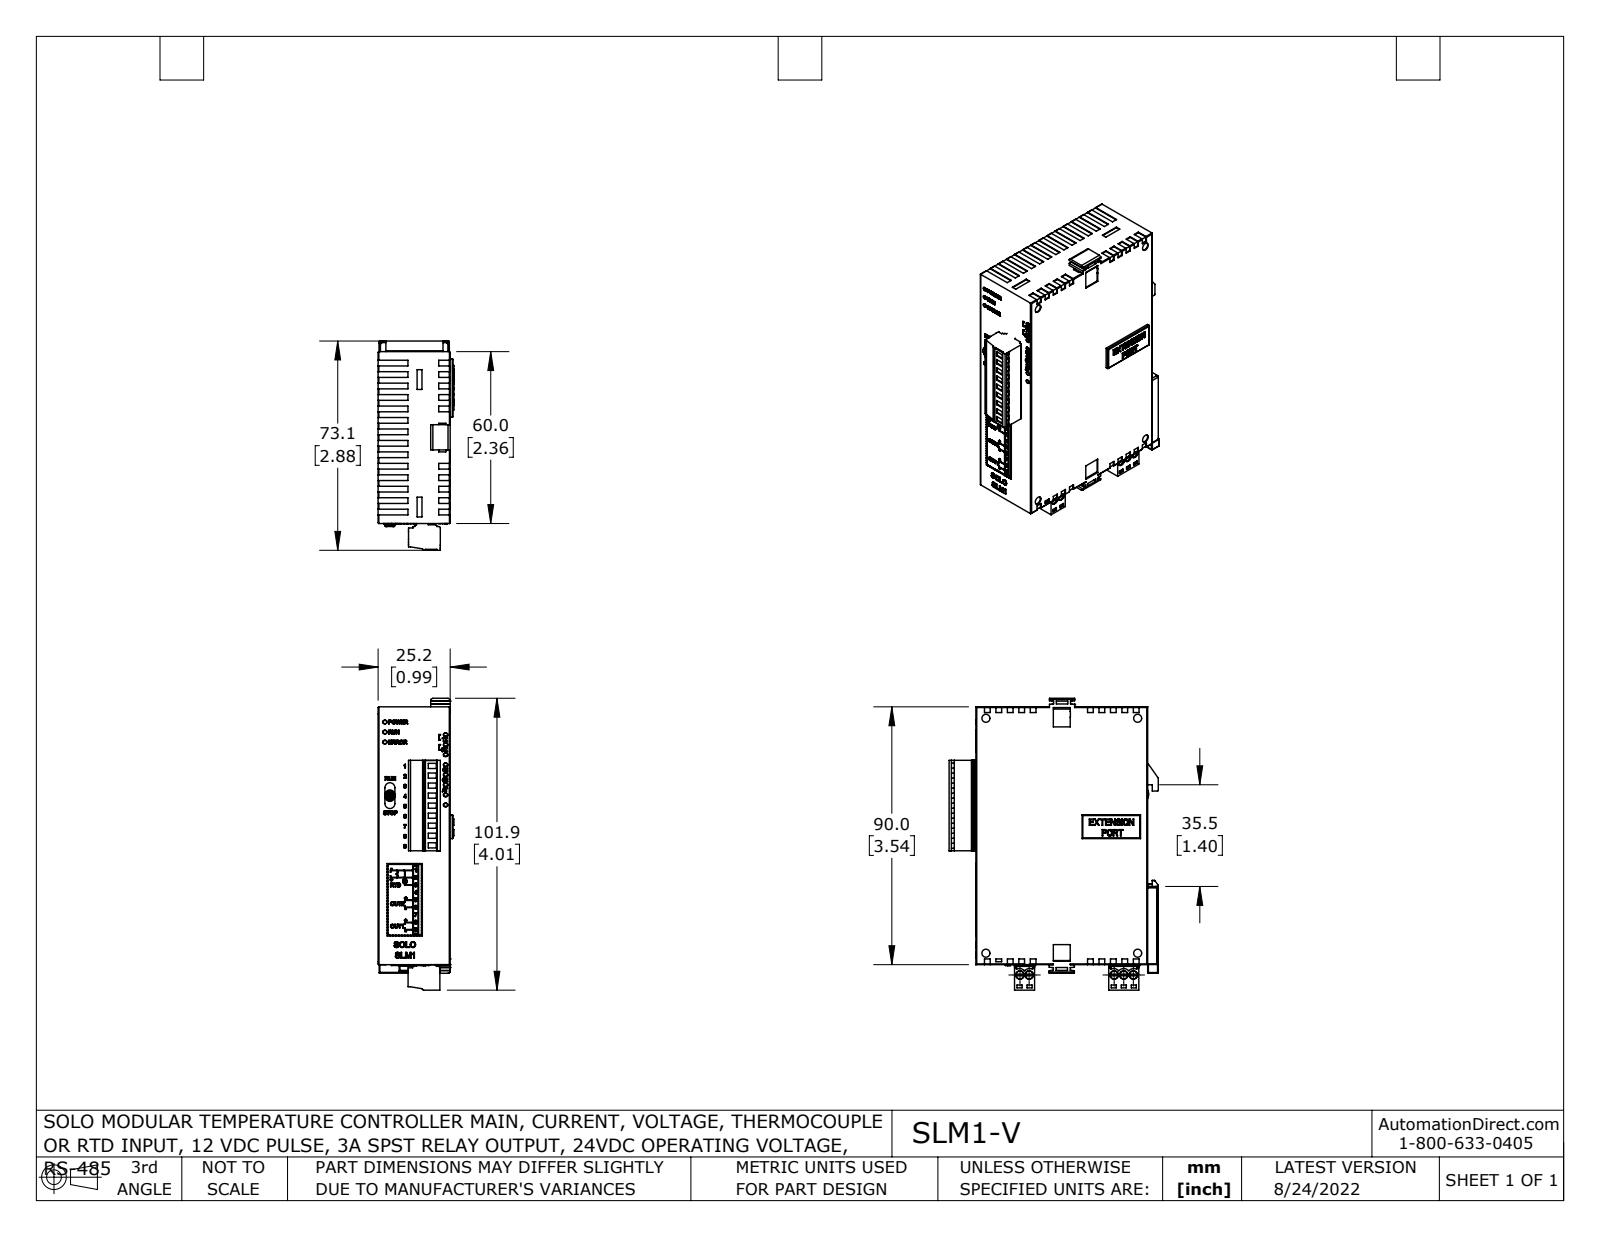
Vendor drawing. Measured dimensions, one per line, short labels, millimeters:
name: SLM1-C sr1 fxt sra coord
written by: SolidWorks 2021 (AUTOMOTIVE_DESIGN)
unit: mm
bodies: 6 solids, 4233 faces (2943 planar, 360 cylindrical, 930 other)
size: 101.9 × 73.1 × 26.5
volume: 142 300 mm³; area: 28 670 mm²
holes: 14× ⌀2.7, 5× ⌀2.9, 4× ⌀2.8, 1× ⌀2.4
bosses: 1× ⌀2.5
rounds: 62× R0.3, 24× R0.6, 22× R0.6, 14× R2.3, 9× R1.5, 7× R0.3, 6× R0.5, 6× R0.5
face distances: 25.2, 59.7, 60, 0.5, 24.7, 90, 89.7, 3.7, 63.7, 1
hole spacings: 6.9, 3.4, 13.7, 3.5, 10.2, 10.3, 20.5, 17
